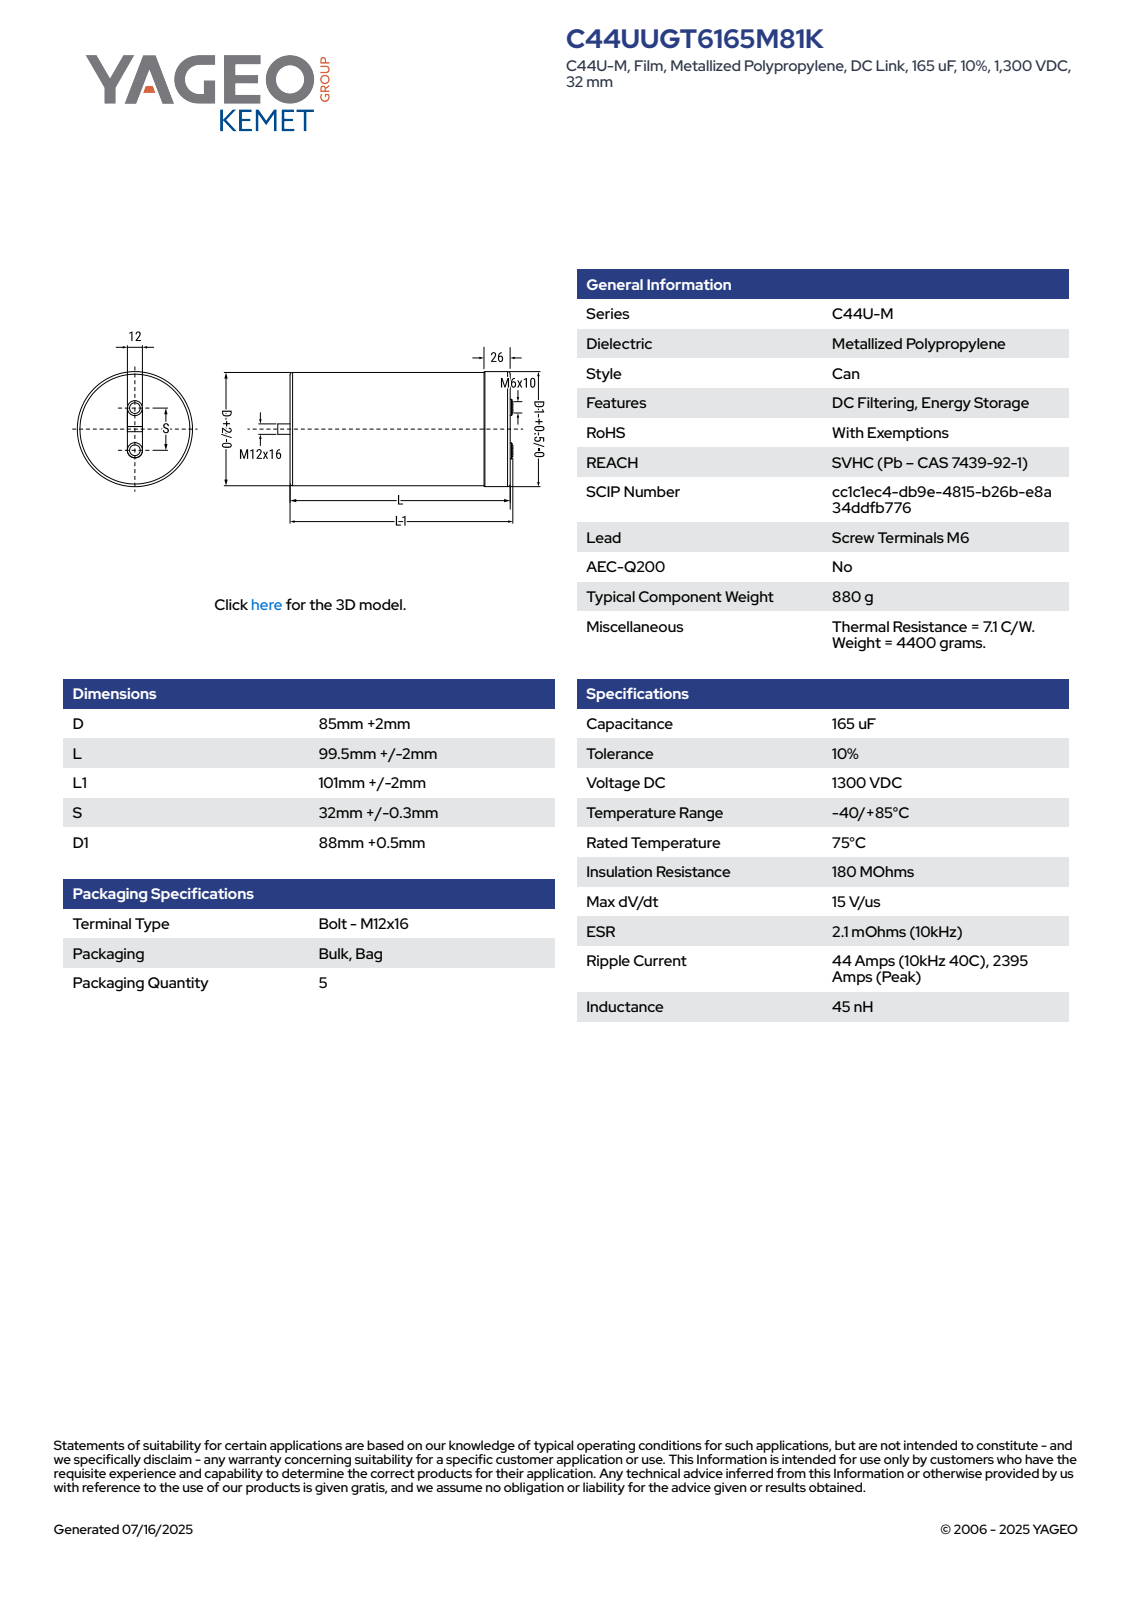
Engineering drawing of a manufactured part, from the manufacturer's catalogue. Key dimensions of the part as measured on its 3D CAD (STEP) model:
Part name (STEP PRODUCT): CFP_C44UMR_85X99.5_D87L101.5S32L1103D188.5
STEP written by: SolidWorks 2014 (AUTOMOTIVE_DESIGN)
Units: millimetres
Bodies: 1 solid, 84 faces (32 planar, 21 cylindrical, 31 other)
Overall size (bounding box): 119 × 88.5 × 88.5
Volume: 610 321 mm³ · Surface area: 41 260 mm²
Round holes (diameter × count): ⌀6 ×2
Round bosses / shafts (diameter × count): ⌀12 ×3, ⌀10 ×2, ⌀88.5 ×1, ⌀87 ×1
Partial cylindrical surfaces — rounded edges, fillets, slot ends (radius × count): R43.51 ×1
Main face-to-face distances: 101.5, 75.5, 26, 16, 91.5, 117.5, 119, 103, 27.5, 1.5
Hole centre spacings: 32
